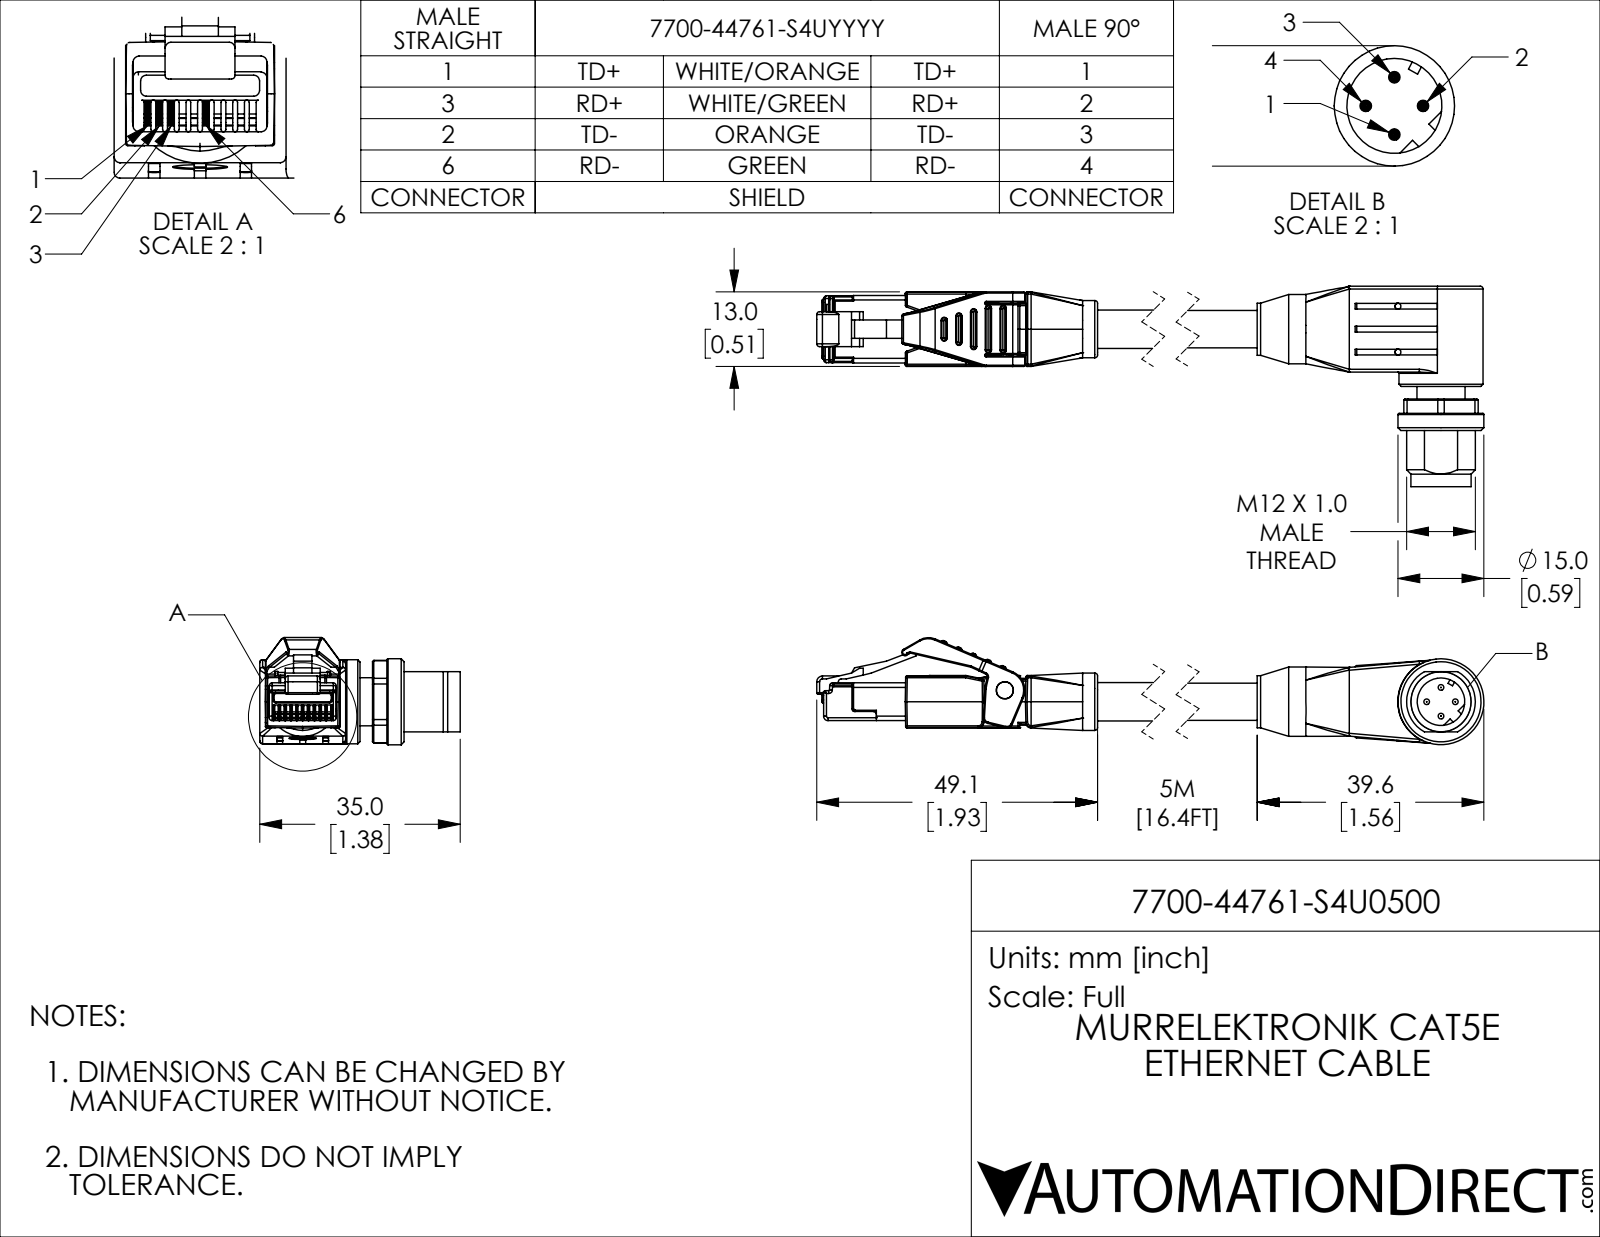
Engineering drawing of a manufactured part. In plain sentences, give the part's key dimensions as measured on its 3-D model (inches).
The part is named "7700-44761-S4U0500; 7700-44761-S4U0500_2; 7700-44761-S4U0500_1". Its 3-D file was written by "SolidWorks 2021 (CONFIG_CONTROL_DESIGN)". It is 3 solids with 883 faces: 369 planar, 338 cylindrical and 176 other. Overall it measures 5.778 by 1.378 by 0.736 inches. Its volume is 0.915 cubic inches and its surface area 11.82 square inches. Round holes: 4 of diameter 0.041, 1 of diameter 0.118, 1 of diameter 0.189, 1 of diameter 0.327. Round bosses or shafts: 4 of diameter 0.039, 1 of diameter 0.591, 1 of diameter 0.579, 1 of diameter 0.476, 1 of diameter 0.413, 1 of diameter 0.394, 1 of diameter 0.358, 1 of diameter 0.331. Partial cylindrical surfaces (rounded edges, fillets, slot ends): 82 of radius 0.008, 67 of radius 0.012, 28 of radius 0.02, 20 of radius 0.004, 5 of radius 0.031, 5 of radius 0.039, 2 of radius 0.079, 2 of radius 0.197. The main face-to-face distances are 0.512, 0.362, 0.039, 0.689, 0.098, 0.551, 0.591, 0.185, 0.077, 0.337. The hole center spacings are 0.315, 4.19.
